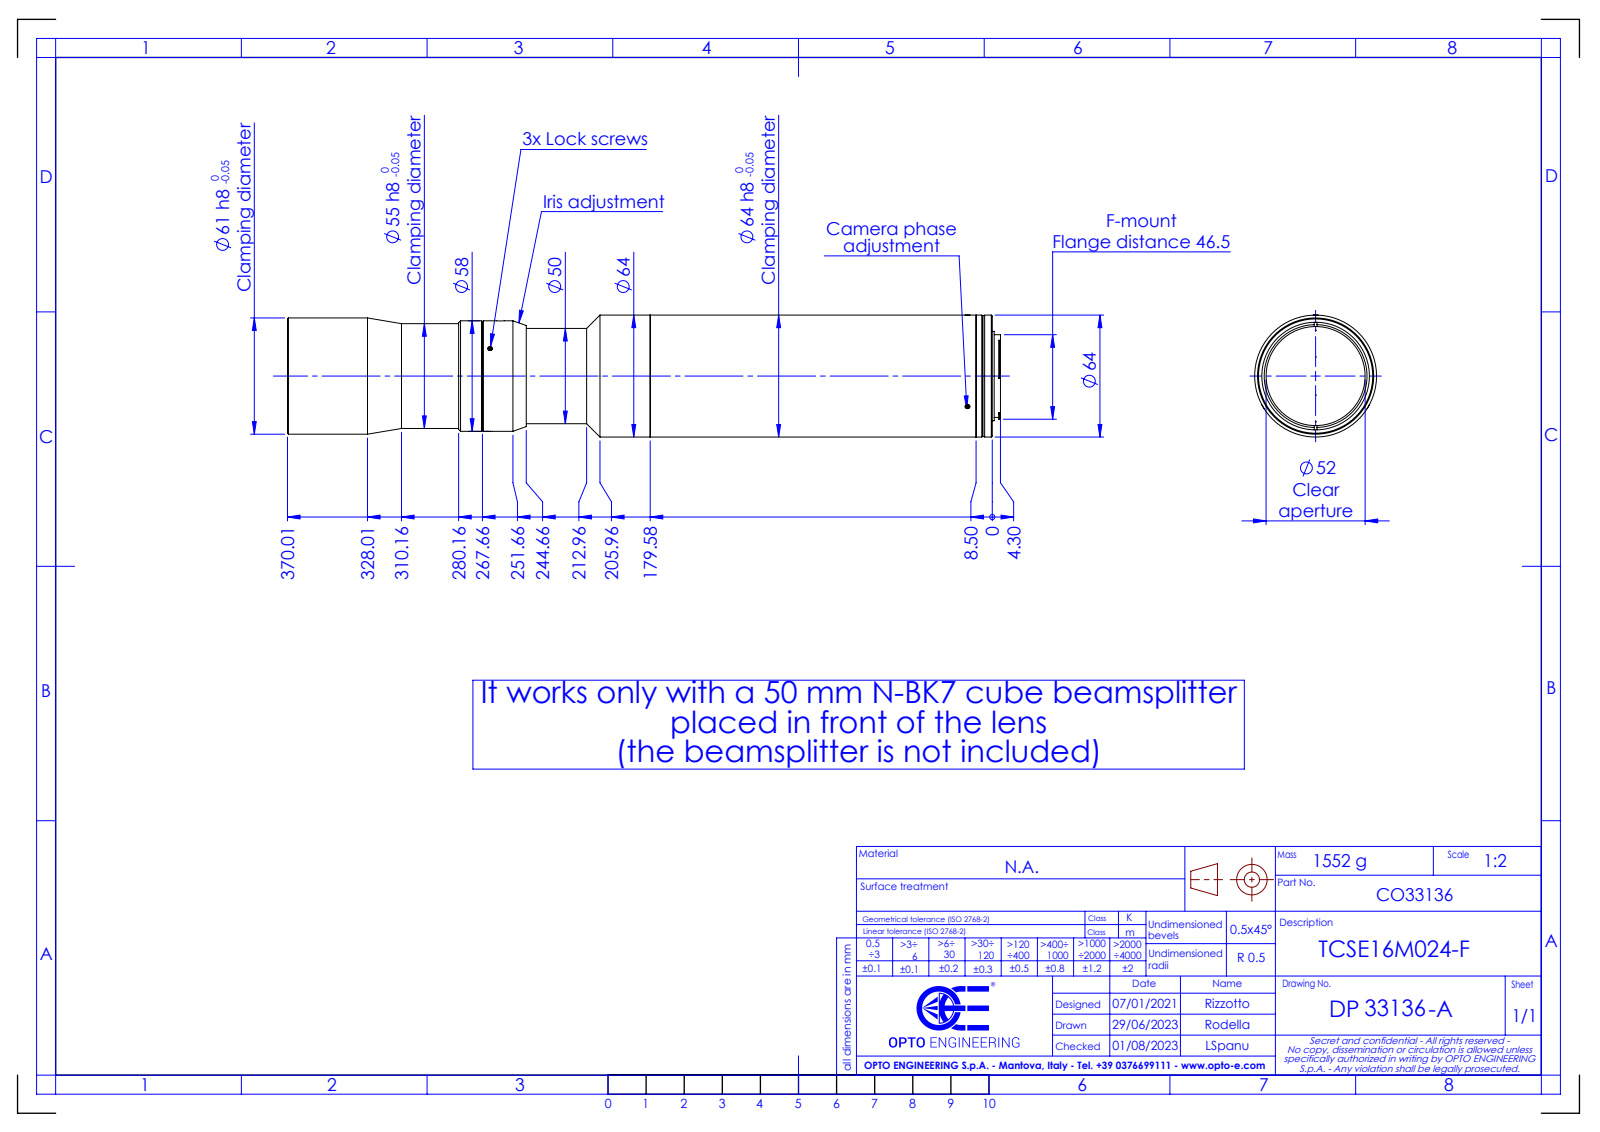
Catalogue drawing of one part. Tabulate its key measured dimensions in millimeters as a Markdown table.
| quantity | value |
| --- | --- |
| part name | DP33136-A_TCSE16M024-F |
| STEP written by | SolidWorks 2021 (CONFIG_CONTROL_DESIGN) |
| units | millimeters |
| bodies | 0 solids, 159 faces (67 planar, 55 cylindrical, 37 other) |
| overall size | 374.31 × 64 × 64 |
| round holes (diameter × count) | 2.5 × 3, 4.2 × 1, 42 × 1, 52 × 1, 54 × 1, 56.5 × 1 |
| round bosses / shafts (diameter × count) | 64 × 1, 63.5 × 1, 61 × 1, 58 × 1, 55 × 1, 50 × 1, 46.9 × 1, 43.4 × 1 |
| partial cylindrical surfaces (radius × count) | 0.5 × 6, 1.15 × 2, 22.65 × 1 |
| main face-to-face distances | 5.5, 1.5, 4, 3, 4.5, 8.5, 271.65, 274.65, 276.15, 280.15 |
| hole center spacings | 5.36 |
